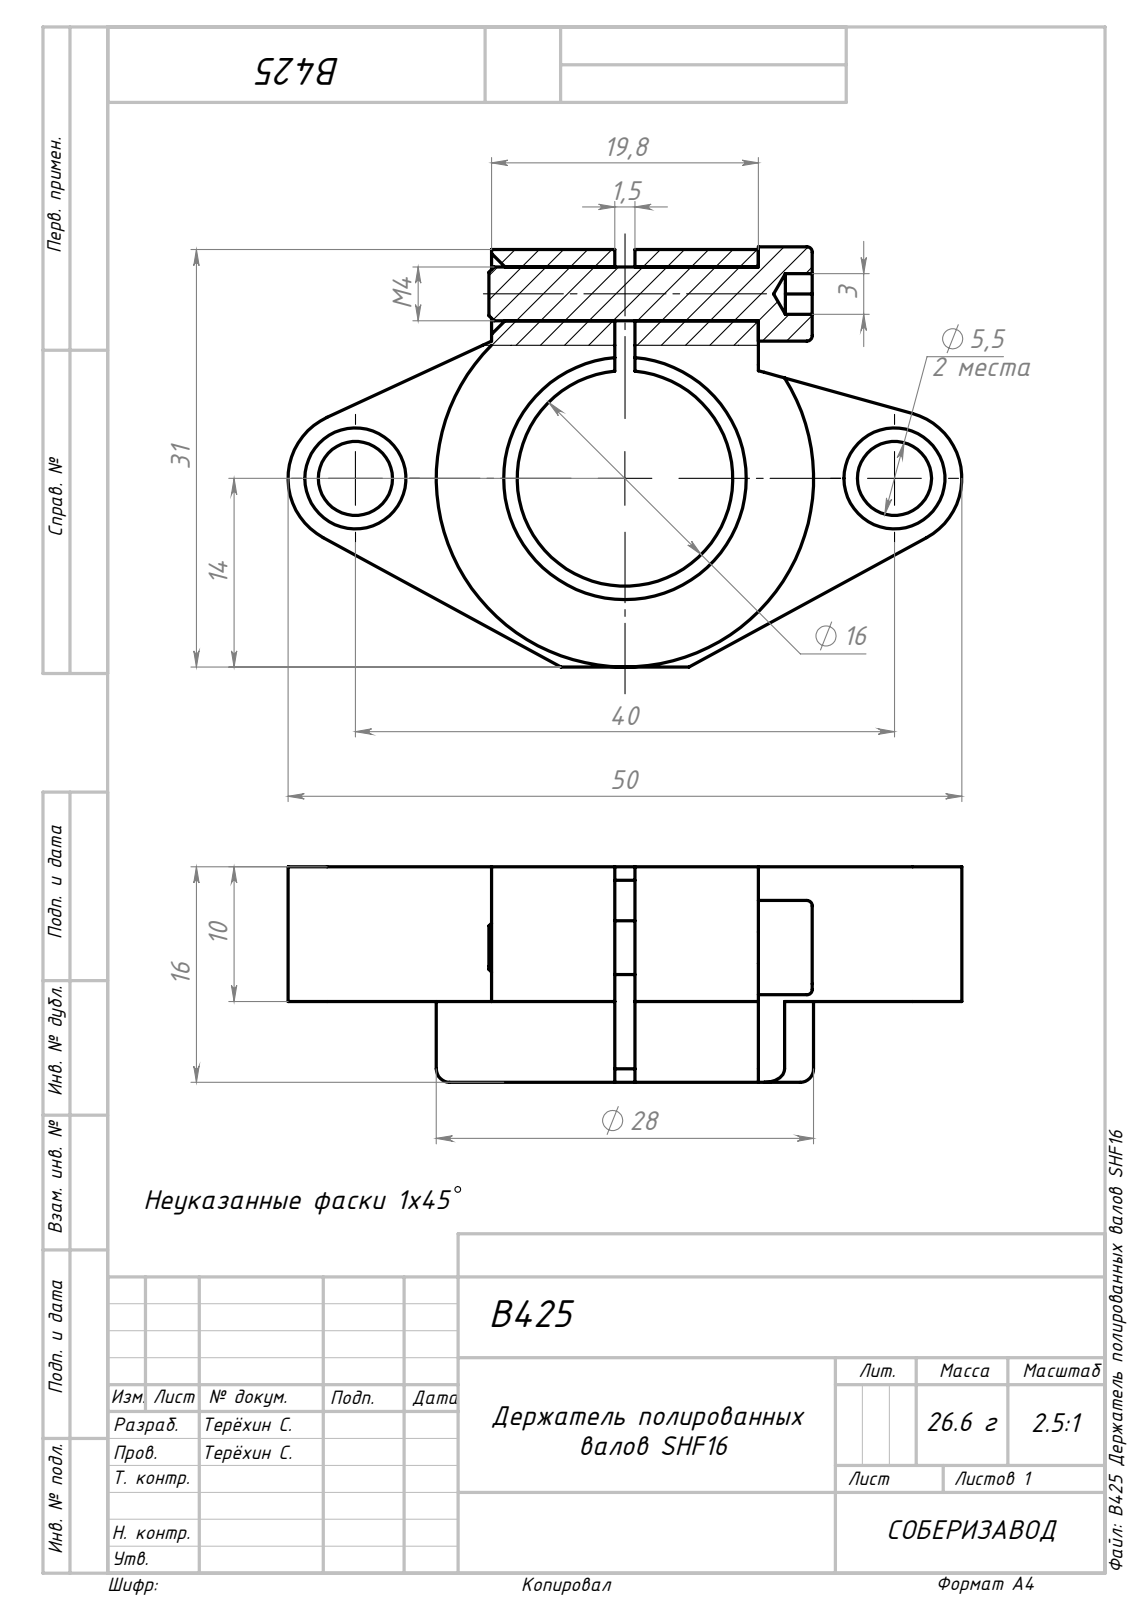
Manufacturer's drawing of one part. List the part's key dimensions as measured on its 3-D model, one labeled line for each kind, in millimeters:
Part name (STEP PRODUCT): B425 Держатель полированных валов SHF16_00; B425 Держатель полированных валов SHF16; socket head cap screw_din_DIN 912 M4 x 20 --- 20N
STEP written by: SolidWorks 2022 (AUTOMOTIVE_DESIGN)
Units: millimetres
Bodies: 2 solids, 81 faces (31 planar, 22 cylindrical, 28 other)
Overall size (bounding box): 50 × 31.2 × 16
Volume: 9 802 mm³ · Surface area: 5 165 mm²
Round holes (diameter × count): ⌀5.5 ×2, ⌀4 ×1, ⌀16 ×1
Round bosses / shafts (diameter × count): ⌀28 ×1, ⌀7 ×1
Partial cylindrical surfaces — rounded edges, fillets, slot ends (radius × count): R5 ×2
Main face-to-face distances: 10, 16, 6, 9.15, 10.65, 1.5, 31, 19.8, 23.8, 14.65
Hole centre spacings: 20, 40
